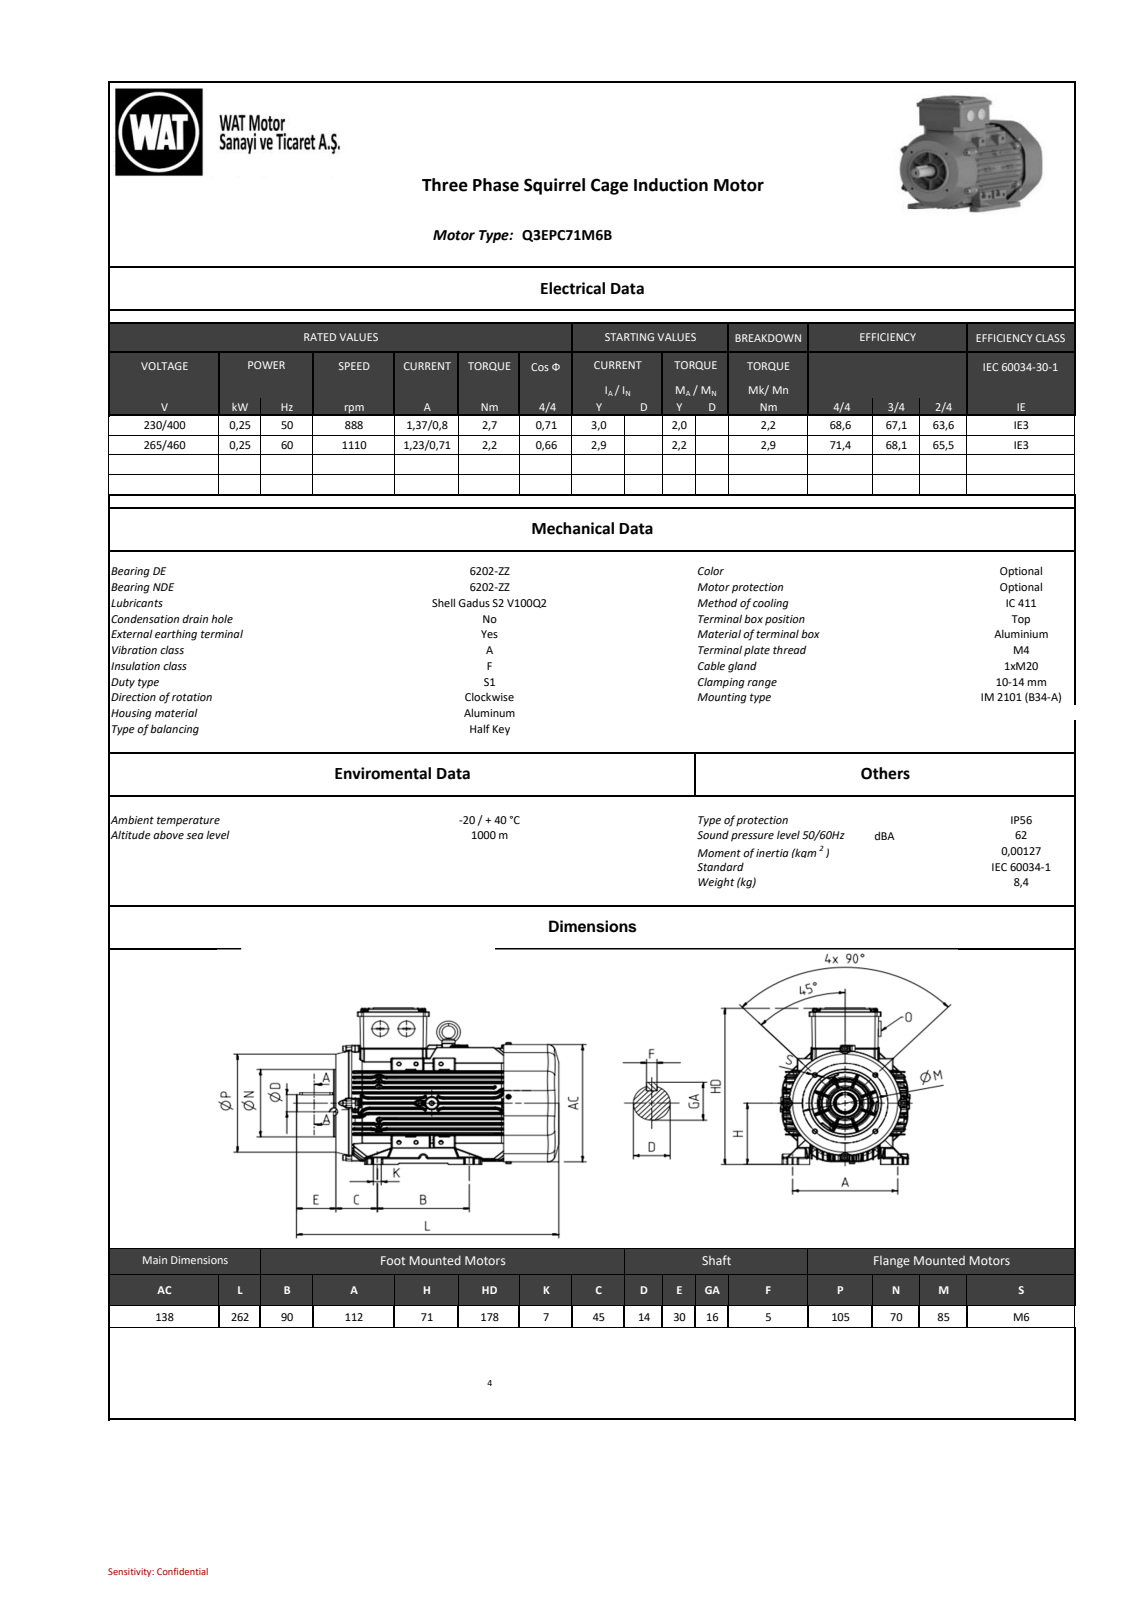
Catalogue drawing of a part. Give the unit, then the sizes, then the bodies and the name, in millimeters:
Units: millimetres
Overall size (bounding box): 262 × 178.11 × 138
Round holes (diameter × count): ⌀3.65 ×8, ⌀3 ×7, ⌀2.5 ×6, ⌀3.3 ×5, ⌀5 ×5, ⌀4 ×4, ⌀4.5 ×4, ⌀4.65 ×4, ⌀4.8 ×4, ⌀5.2 ×4, ⌀7 ×4, ⌀3.7 ×3
Round bosses / shafts (diameter × count): ⌀8 ×8, ⌀4 ×8, ⌀12 ×4, ⌀3.3 ×4, ⌀138 ×1, ⌀70 ×1, ⌀61 ×1, ⌀26 ×1
Partial cylindrical surfaces — rounded edges, fillets, slot ends (radius × count): R1 ×141, R0.5 ×57, R1.2 ×36, R1.5 ×24, R5 ×19, R2 ×17, R4 ×17, R3.25 ×16
Main face-to-face distances: 3, 2, 1, 5, 194.5, 4, 15, 83, 35, 172
Hole centre spacings: 61.39, 87.43, 55, 36.59, 67.18, 67.2, 92.35, 60
Bodies: 0 solids, 2947 faces (1462 planar, 795 cylindrical, 690 other)
Part name (STEP PRODUCT): 001_objects
STEP written by: SIEMENS PLM Software NX2206.8101 (AUTOMOTIVE_DESIGN)
